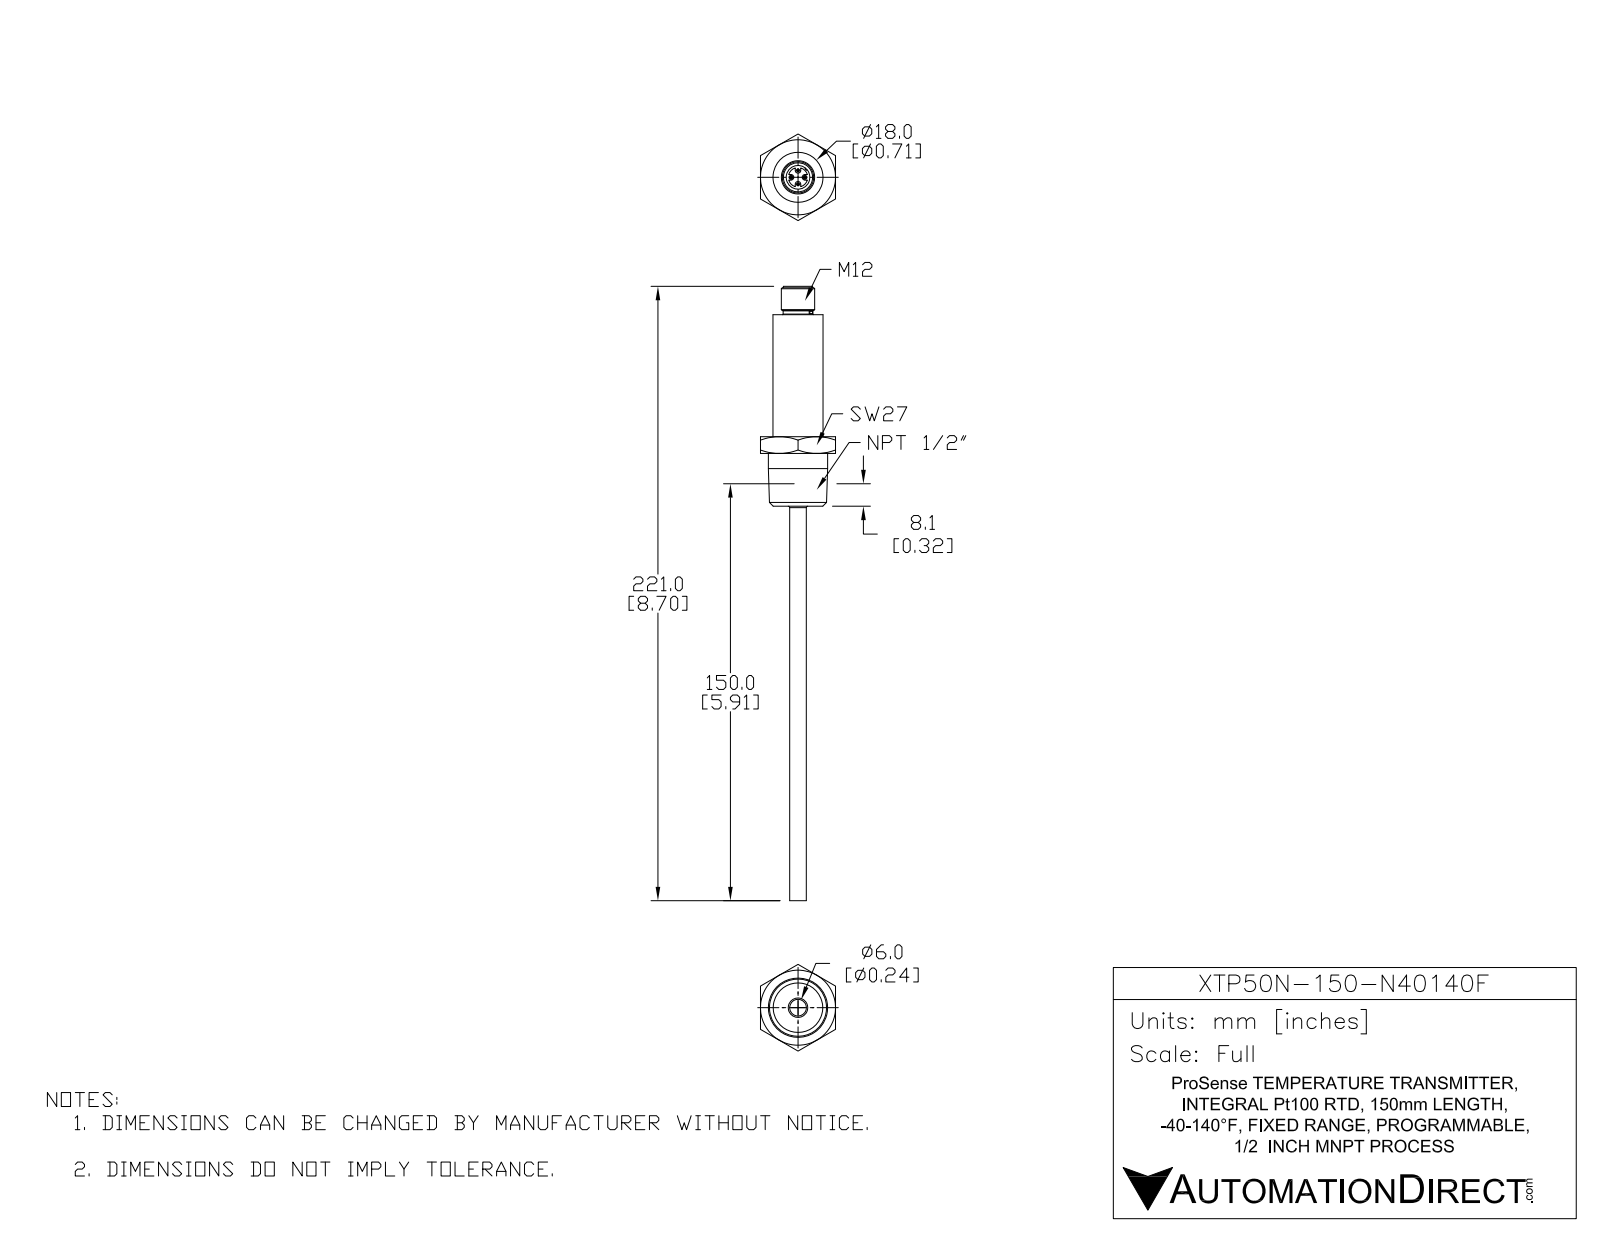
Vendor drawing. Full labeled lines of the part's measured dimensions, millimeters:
Part name (STEP PRODUCT): XTP50N-150-N40140F
STEP written by: SolidWorks 2015 (AUTOMOTIVE_DESIGN)
Units: millimetres
Bodies: 1 solid, 117 faces (43 planar, 34 cylindrical, 40 other)
Overall size (bounding box): 221 × 31.18 × 27
Volume: 25 748 mm³ · Surface area: 9 159 mm²
Round holes (diameter × count): ⌀4 ×1, ⌀8.5 ×1
Round bosses / shafts (diameter × count): ⌀1.02 ×4, ⌀21.34 ×1, ⌀18 ×1, ⌀12 ×1, ⌀10.7 ×1, ⌀10.5 ×1, ⌀6 ×1
Partial cylindrical surfaces — rounded edges, fillets, slot ends (radius × count): R1 ×4, R3.5 ×1, R4.25 ×1
Main face-to-face distances: 27, 25, 19, 6, 68.9, 49.9, 43.9, 79.1, 60.1, 54.1
